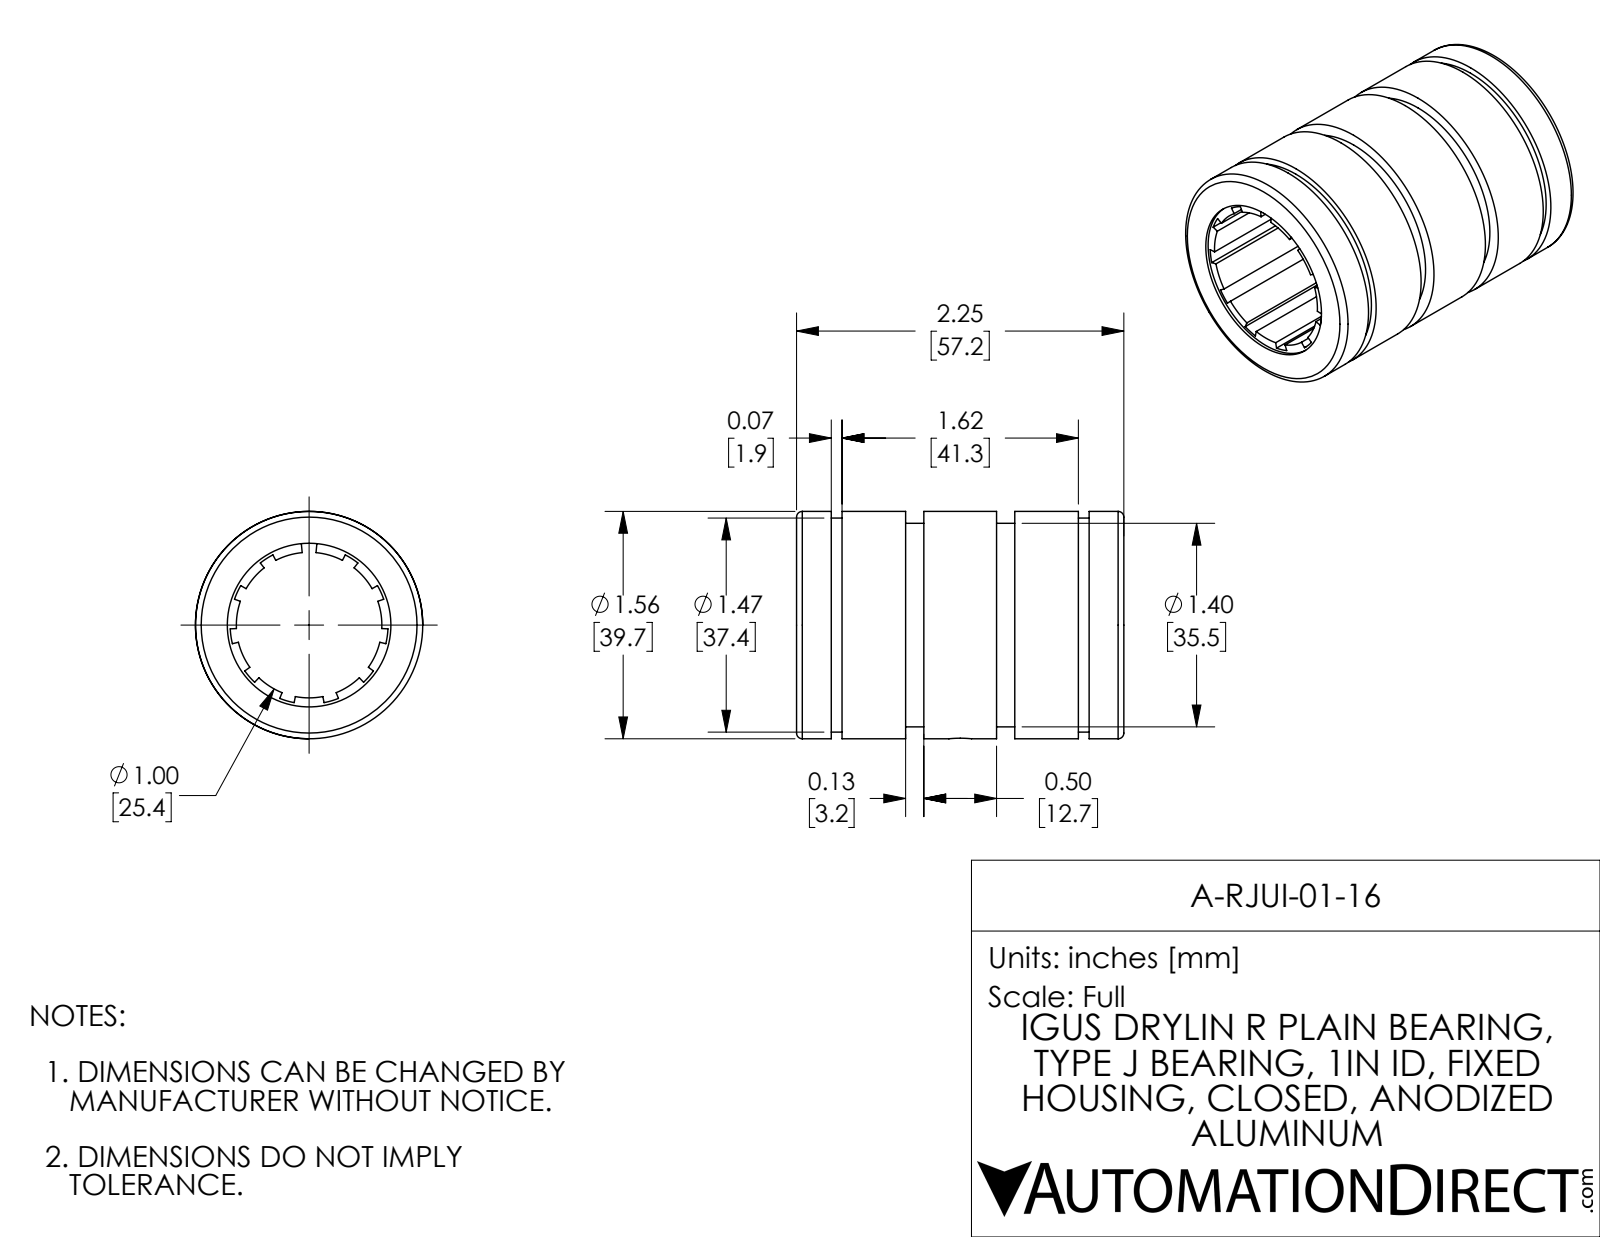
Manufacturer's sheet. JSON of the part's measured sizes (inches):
{"part_name": "A-RJUI-01-16", "step_written_by": "SolidWorks 2017 (AUTOMOTIVE_DESIGN)", "units": "inches", "bodies": {"solids": 2, "faces": 147, "planar": 79, "cylindrical": 64, "other": 4}, "overall_size": [2.25, 1.563, 1.563], "volume_in3": 2.287, "surface_area_in2": 40.55, "round_holes": [[0.156, 1], [1.125, 1], [1.203, 1]], "round_bosses_or_shafts": [[1.563, 1], [1.471, 1], [1.399, 1], [1.125, 1], [0.15, 1]], "partial_cylinders_radius": [[0.5, 1], [0.543, 1], [0.594, 1]], "face_to_face_distances": [0.75, 0.875, 1.375, 1.5, 0.625, 0.125, 2.25, 1.031, 1.219, 0.281]}
